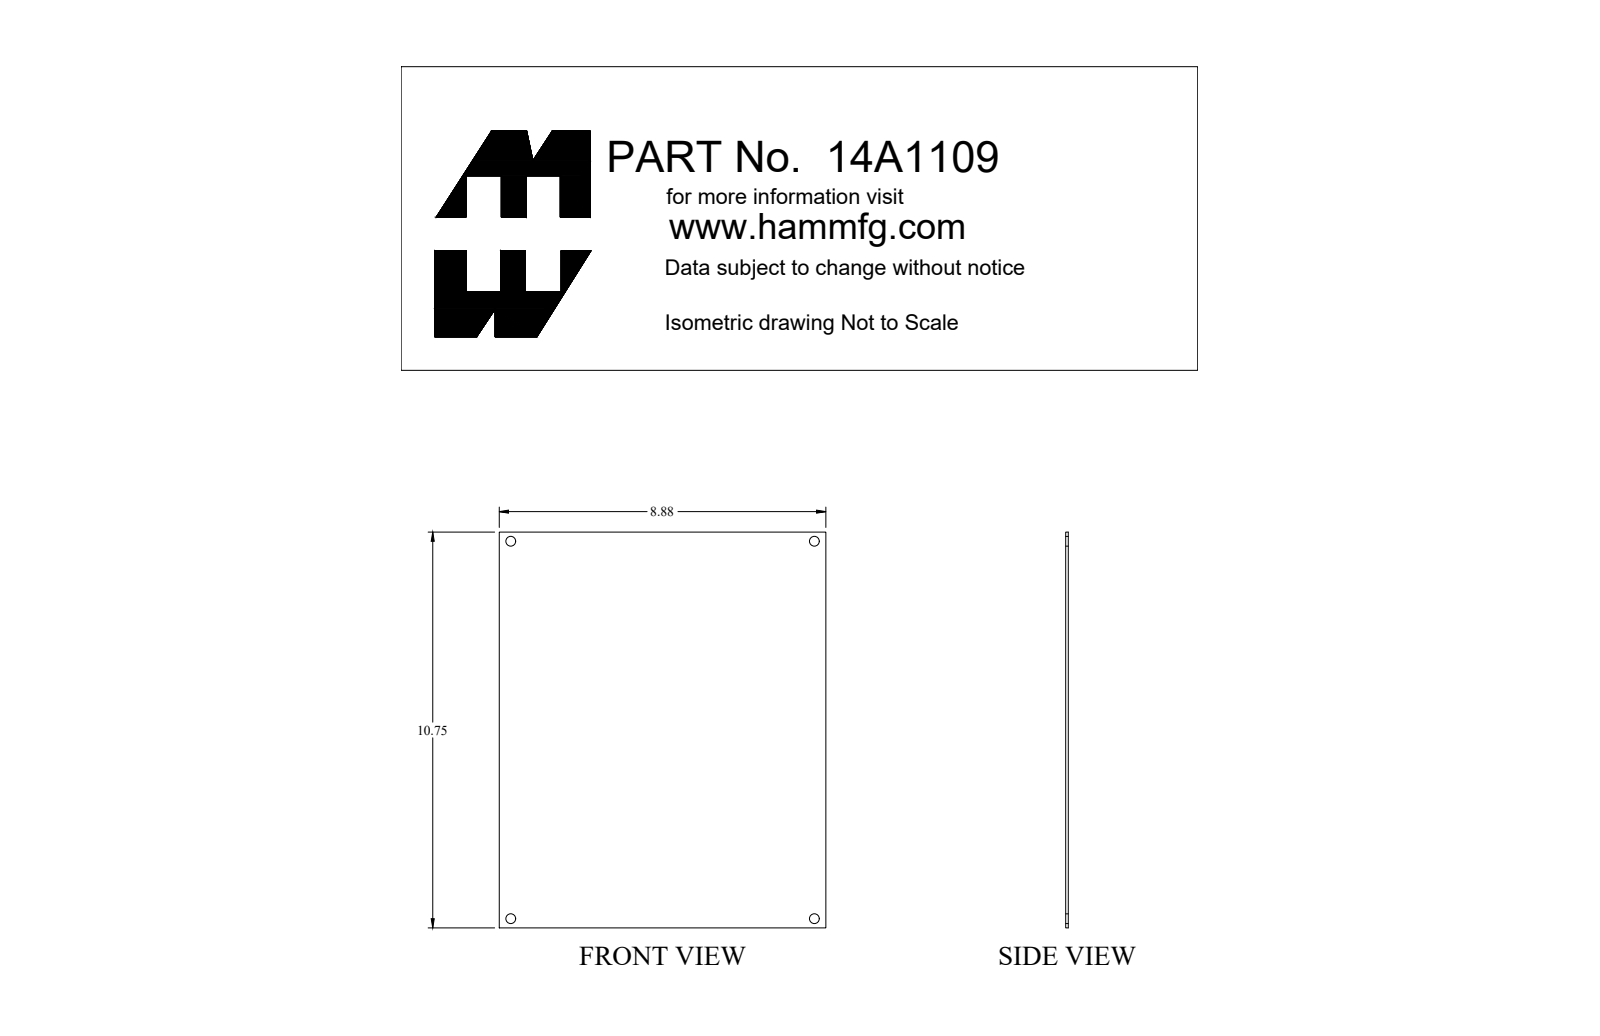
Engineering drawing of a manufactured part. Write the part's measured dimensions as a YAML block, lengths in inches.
part_name: "14A1109"
step_written_by: "SolidWorks 2018 (AUTOMOTIVE_DESIGN)"
units: inches
bodies: {solids: 1, faces: 10, planar: 6, cylindrical: 4, other: 0}
overall_size: [10.75, 8.875, 0.072]
volume: 6.853
surface_area: 193.4
round_holes:
  - {diameter: 0.265, count: 4}
face_to_face_distances: [0.072, 8.875, 10.75]
hole_center_spacings: [8.25, 10.25, 13.158]
